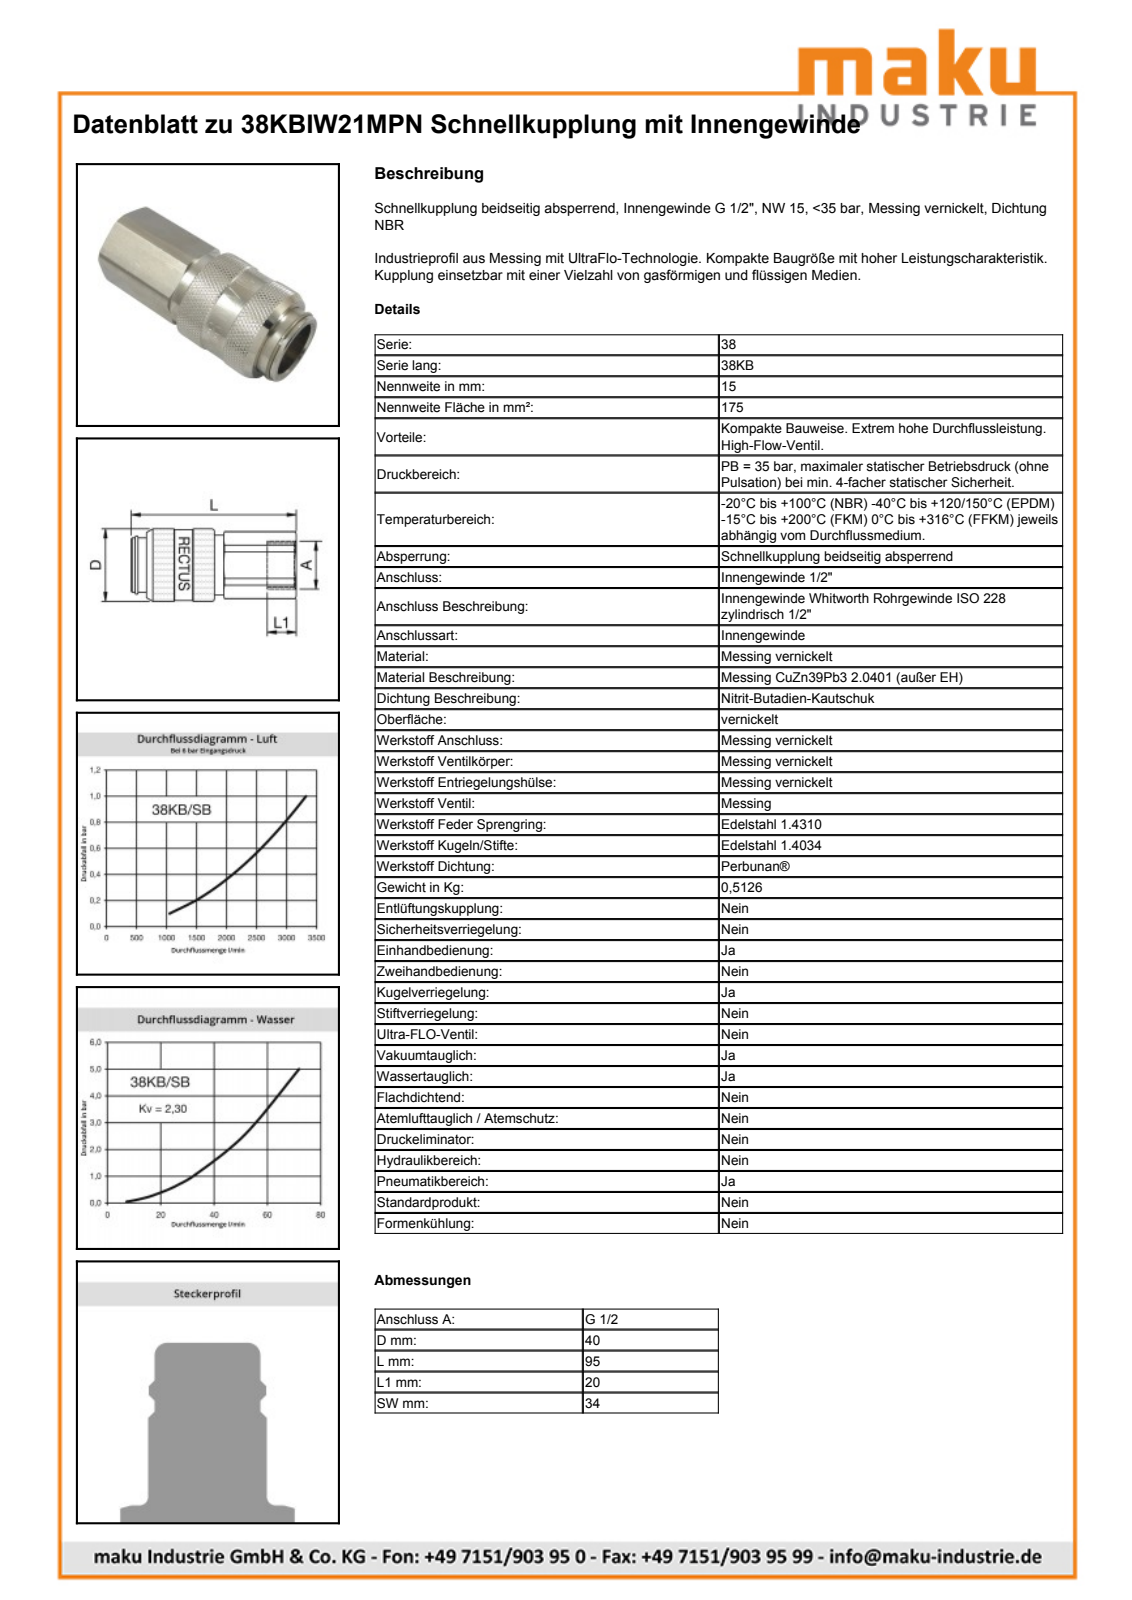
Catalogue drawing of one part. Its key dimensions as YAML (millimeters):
part_name: "D104483"
step_written_by: "Autodesk Inventor 2013 (AUTOMOTIVE_DESIGN)"
units: millimeters
bodies: {solids: 2, faces: 519, planar: 185, cylindrical: 75, other: 259}
overall_size: [91.05, 40, 40]
volume: 86585
surface_area: 22782
round_holes:
  - {diameter: 18.63, count: 1}
  - {diameter: 30, count: 1}
  - {diameter: 30.75, count: 1}
  - {diameter: 34.45, count: 1}
  - {diameter: 34.6, count: 1}
round_bosses_or_shafts:
  - {diameter: 40, count: 1}
  - {diameter: 39, count: 1}
  - {diameter: 34, count: 1}
  - {diameter: 28.5, count: 1}
  - {diameter: 28.43, count: 1}
partial_cylinders:
  - {radius: 18.5, count: 1}
  - {radius: 19.4, count: 1}
face_to_face_distances: [34.02, 34, 91.05, 8.15, 82.9, 19.05, 72, 63.85, 29.65, 21.5]
